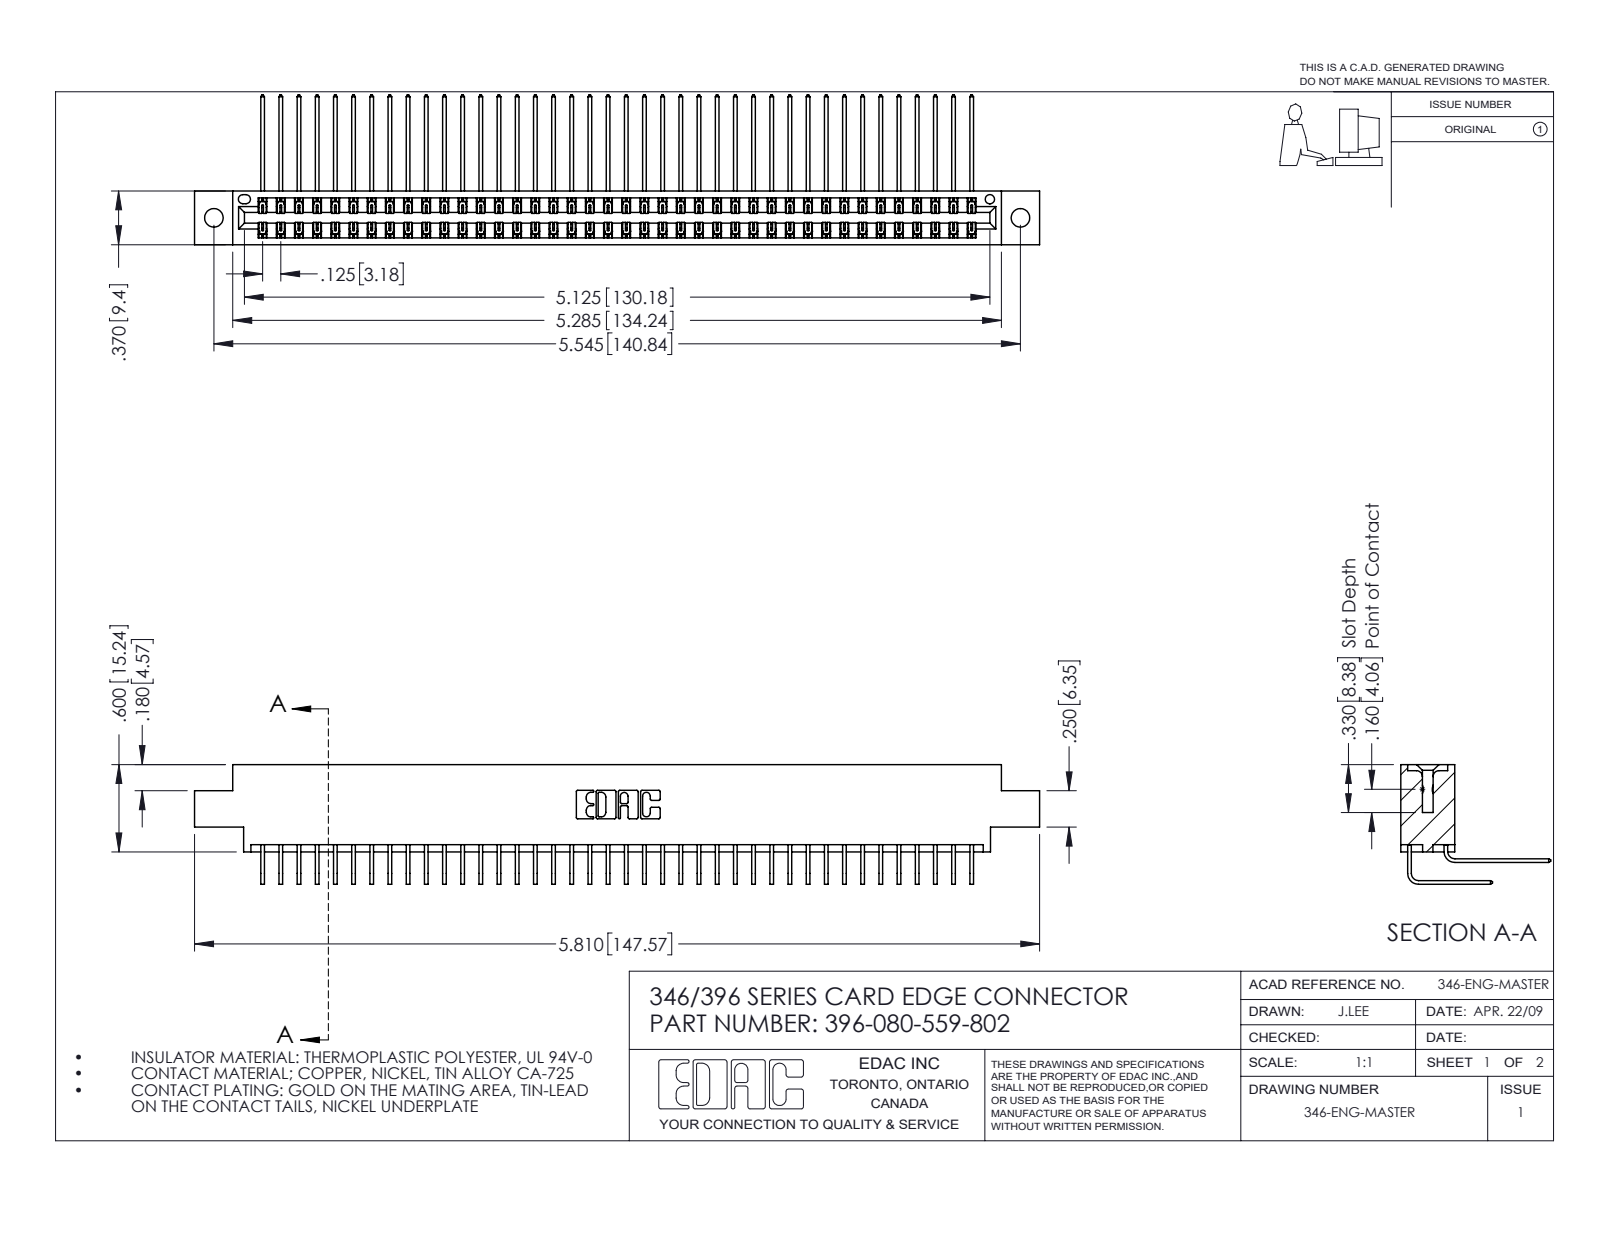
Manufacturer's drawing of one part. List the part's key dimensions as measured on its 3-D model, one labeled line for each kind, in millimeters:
Part name (STEP PRODUCT): 396-080-559-802; 346 Part_0.170 Offset - 0.128 Dia; 345-292-001_558 559 Tail - 1; 345-292-001_559 Tail - 2
STEP written by: SolidWorks 2016 (CONFIG_CONTROL_DESIGN)
Units: millimetres
Bodies: 81 solids, 4446 faces (3040 planar, 1406 cylindrical, 0 other)
Overall size (bounding box): 147.6 × 26.2 × 20.9
Volume: 14 700 mm³ · Surface area: 22 230 mm²
Round holes (diameter × count): ⌀3.3 ×2, ⌀1.6 ×1
Partial cylindrical surfaces — rounded edges, fillets, slot ends (radius × count): R0.2 ×120, R0.3 ×22, R0.2 ×6, R0.8 ×6, R0.7 ×3, R0.4 ×2, R0.6 ×2, R0.6 ×2
Main face-to-face distances: 1.2, 8.2, 0.6, 9.4, 6.4, 1.8, 7.6, 7, 3.8, 5.6
Hole centre spacings: 6.2, 135.5, 140.8
